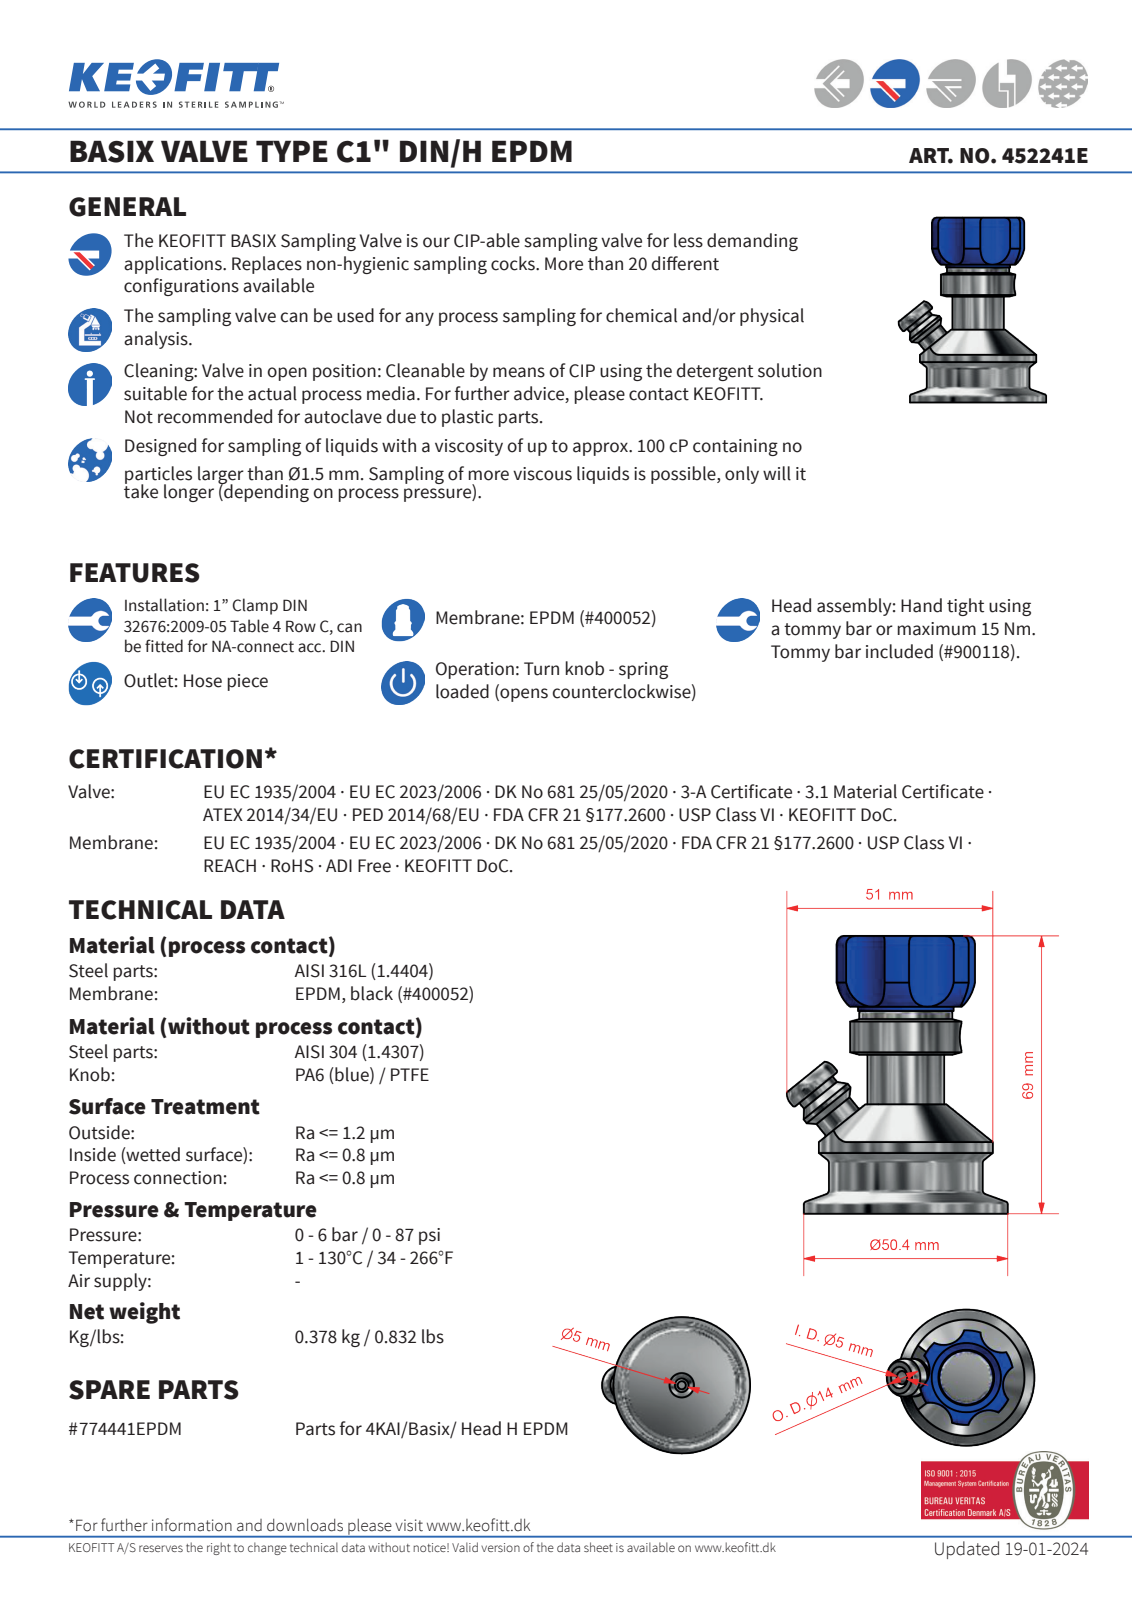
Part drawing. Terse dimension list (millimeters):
name: 452241E
written by: Autodesk Inventor 2020 (AUTOMOTIVE_DESIGN)
unit: mm
bodies: 1 solid, 107 faces (20 planar, 43 cylindrical, 44 other)
size: 68.5 × 54.6 × 50.4
volume: 54 612 mm³; area: 15 059 mm²
holes: 2× ⌀5, 1× ⌀6.05, 1× ⌀16.5, 1× ⌀18.5, 1× ⌀18.6, 1× ⌀19.6, 1× ⌀20.6
bosses: 3× ⌀14, 1× ⌀50.4, 1× ⌀43, 1× ⌀38, 1× ⌀27.5, 1× ⌀23.6, 1× ⌀23, 1× ⌀20
rounds: 8× R8, 1× R17.5
face distances: 50, 51.04, 1.04, 68.5, 18.5, 17.46, 2, 39.2, 10.8, 11.84
